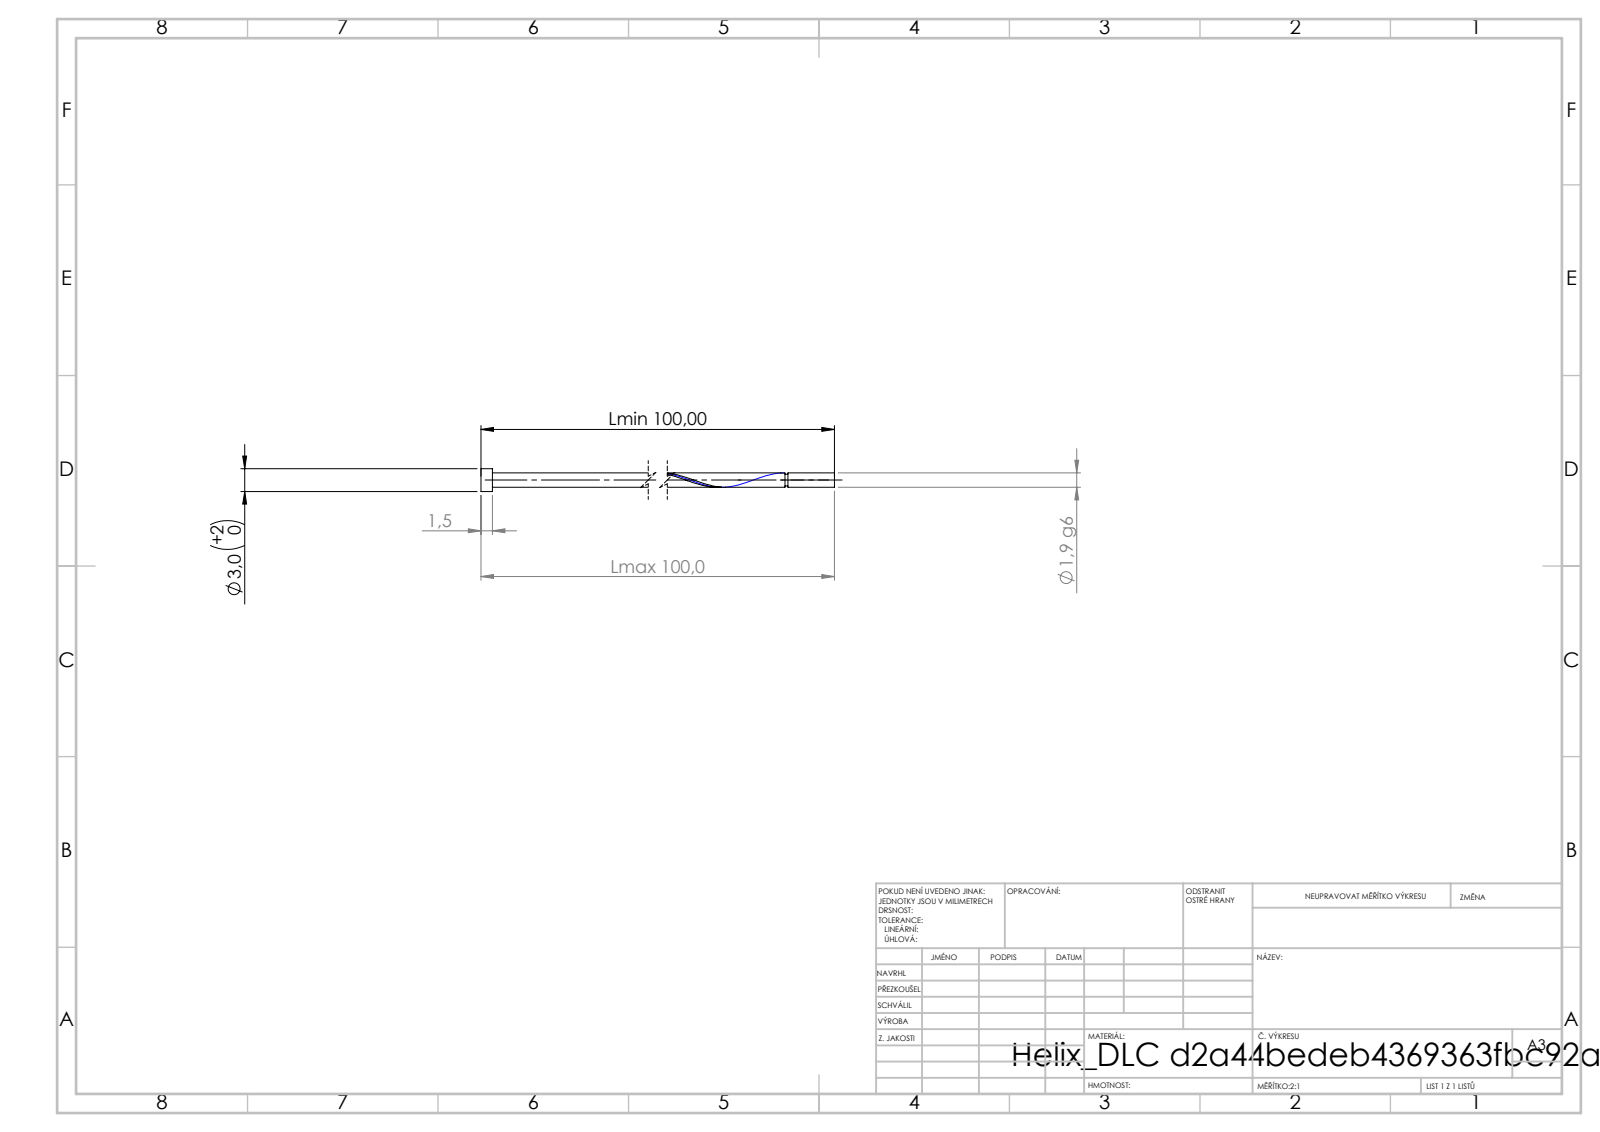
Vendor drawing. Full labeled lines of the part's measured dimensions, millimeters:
STEP written by: SolidWorks 2019 (CONFIG_CONTROL_DESIGN)
Units: millimetres
Bodies: 1 solid, 16 faces (6 planar, 9 cylindrical, 1 other)
Overall size (bounding box): 100 × 3 × 3
Volume: 350 mm³ · Surface area: 826 mm²
Round bosses / shafts (diameter × count): ⌀3 ×1, ⌀1.9 ×1, ⌀1.52 ×1
Main face-to-face distances: 1.5, 100, 98.5, 93.89, 92.39, 6.11, 93.51, 92.01, 0.38, 6.49
